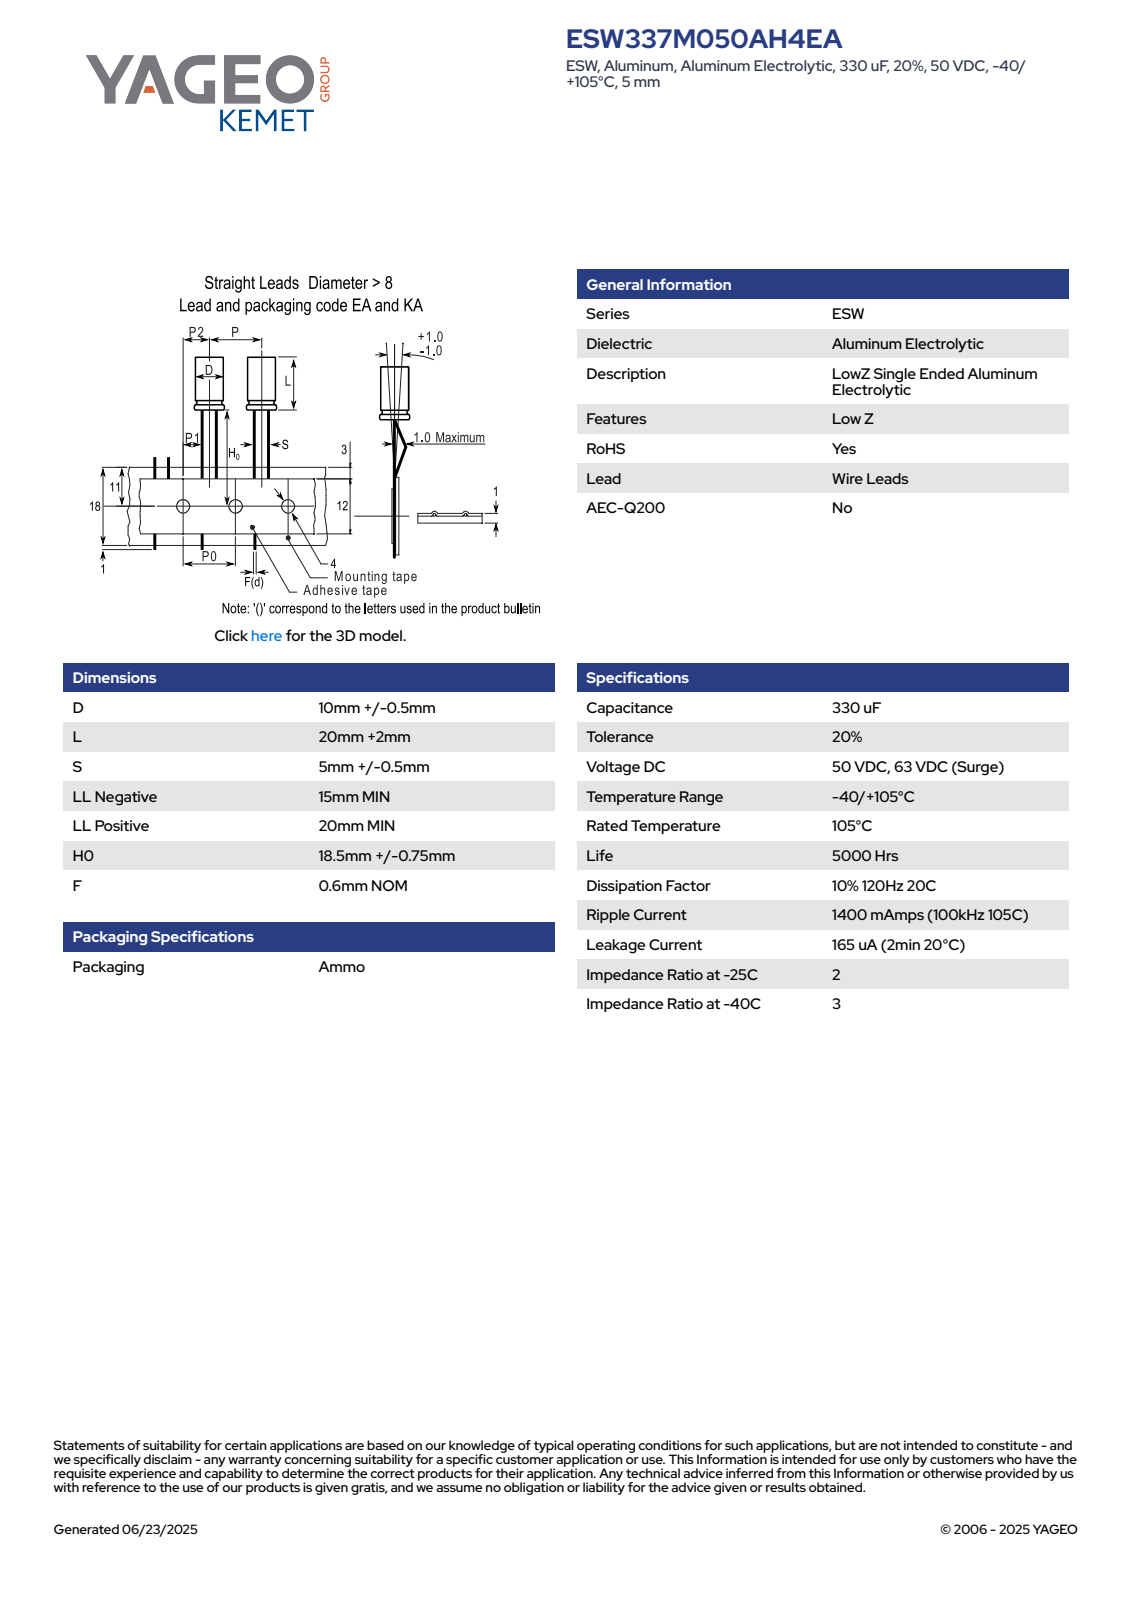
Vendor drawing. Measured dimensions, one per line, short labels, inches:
name: CAR_KTRL_10X20_D10.5L22S5F0.6
written by: SolidWorks 2014 (AUTOMOTIVE_DESIGN)
unit: in
bodies: 4 solids, 73 faces (61 planar, 8 cylindrical, 4 other)
size: 1.654 × 0.413 × 0.413
volume: 0.116 in³; area: 1.53 in²
bosses: 2× ⌀0.024, 1× ⌀0.413
face distances: 0.866, 0.867, 1.457, 1.457, 0.591, 1.654, 1.654, 0.787, 0.197, 0.049
